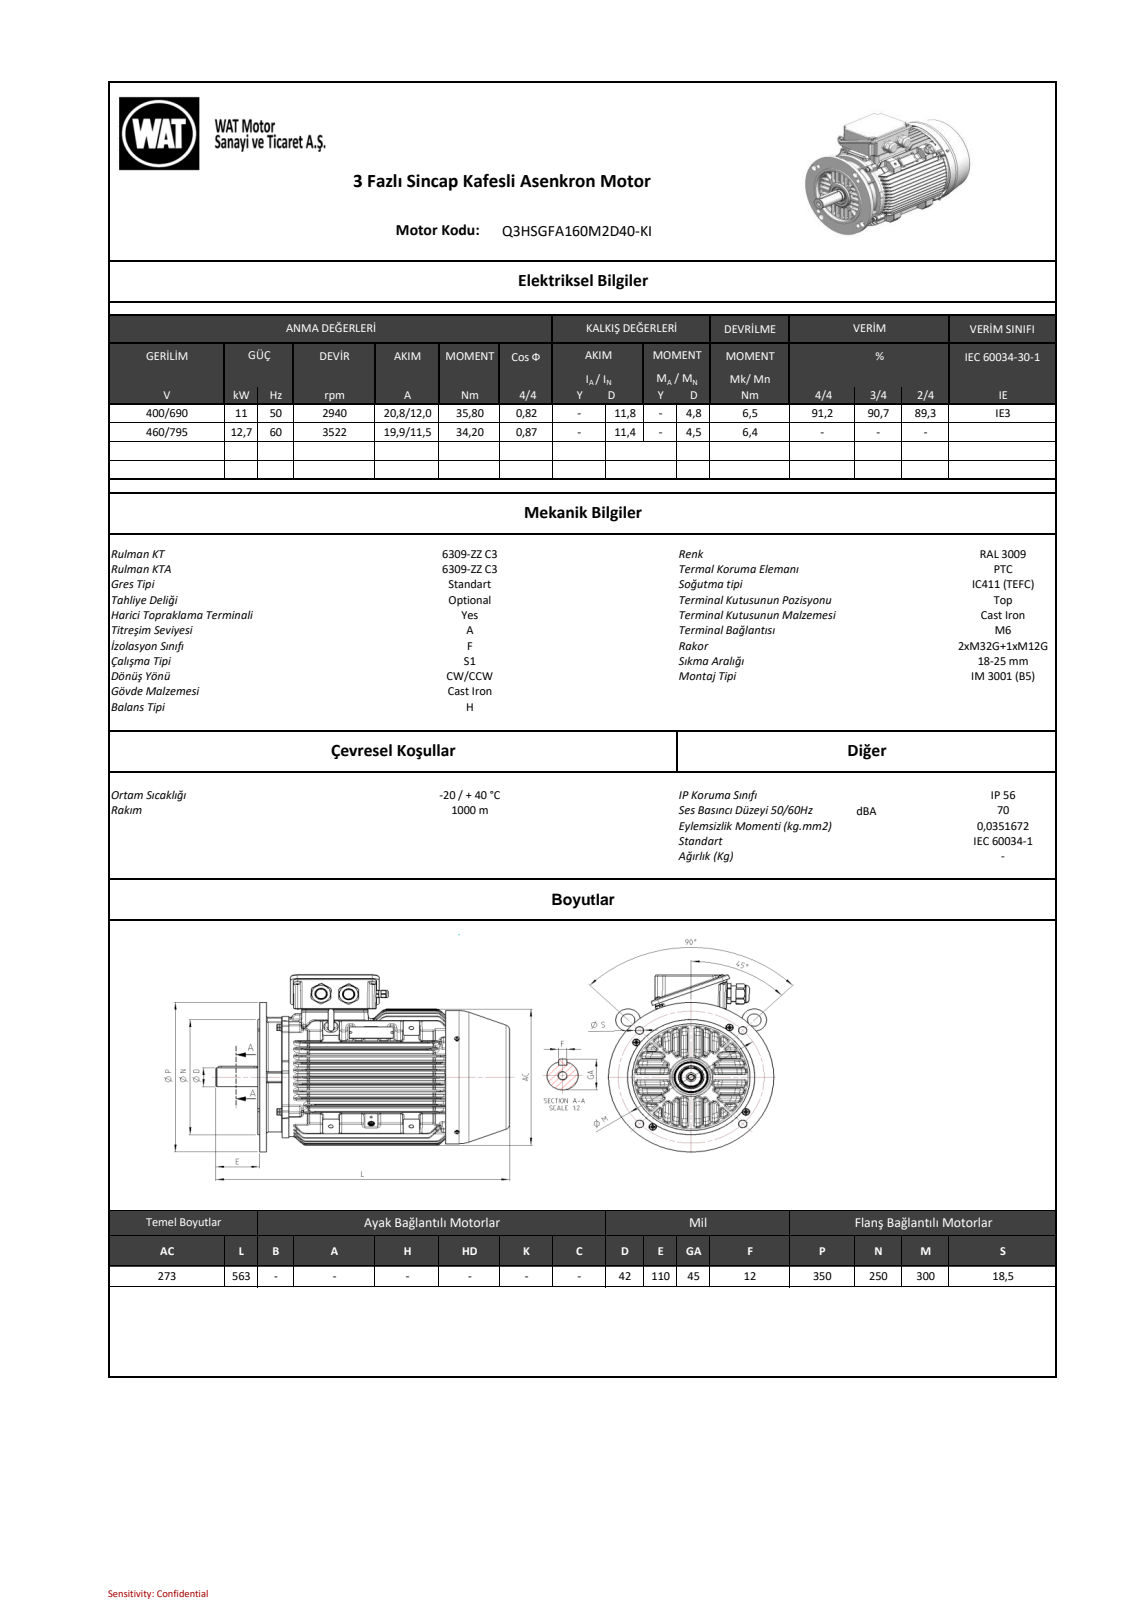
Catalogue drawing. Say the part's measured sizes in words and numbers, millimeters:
The part is named "C9017F38B806sw8k". Its 3-D file was written by "SIEMENS PLM Software NX 11.0 (AUTOMOTIVE_DESIGN)". It is 0 solids with 5730 faces: 1075 planar, 1475 cylindrical and 3180 other. Overall it measures 563 by 380.49 by 349 millimeters. Round holes: 8 of diameter 6.8, 6 of diameter 8.5, 4 of diameter 15, 2 of diameter 4.2, 2 of diameter 10, 2 of diameter 19, 2 of diameter 21, 1 of diameter 2.5, 1 of diameter 6, 1 of diameter 11.3, 1 of diameter 13, 1 of diameter 24.5. Round bosses or shafts: 4 of diameter 10, 4 of diameter 8.65, 4 of diameter 8, 4 of diameter 5, 2 of diameter 36, 2 of diameter 34.5, 2 of diameter 31.25, 2 of diameter 25. Partial cylindrical surfaces (rounded edges, fillets, slot ends): 263 of radius 4, 146 of radius 3, 106 of radius 1.5, 84 of radius 2, 64 of radius 1.8, 24 of radius 28, 24 of radius 37, 24 of radius 44. The main face-to-face distances are 6.5, 13.83, 13.76, 27.59, 41.49, 27.73, 13.9, 55.44, 41.68, 27.85. The hole center spacings are 73.55, 121.5, 171.83, 42.2, 139.38, 146, 199.06, 239.31.
